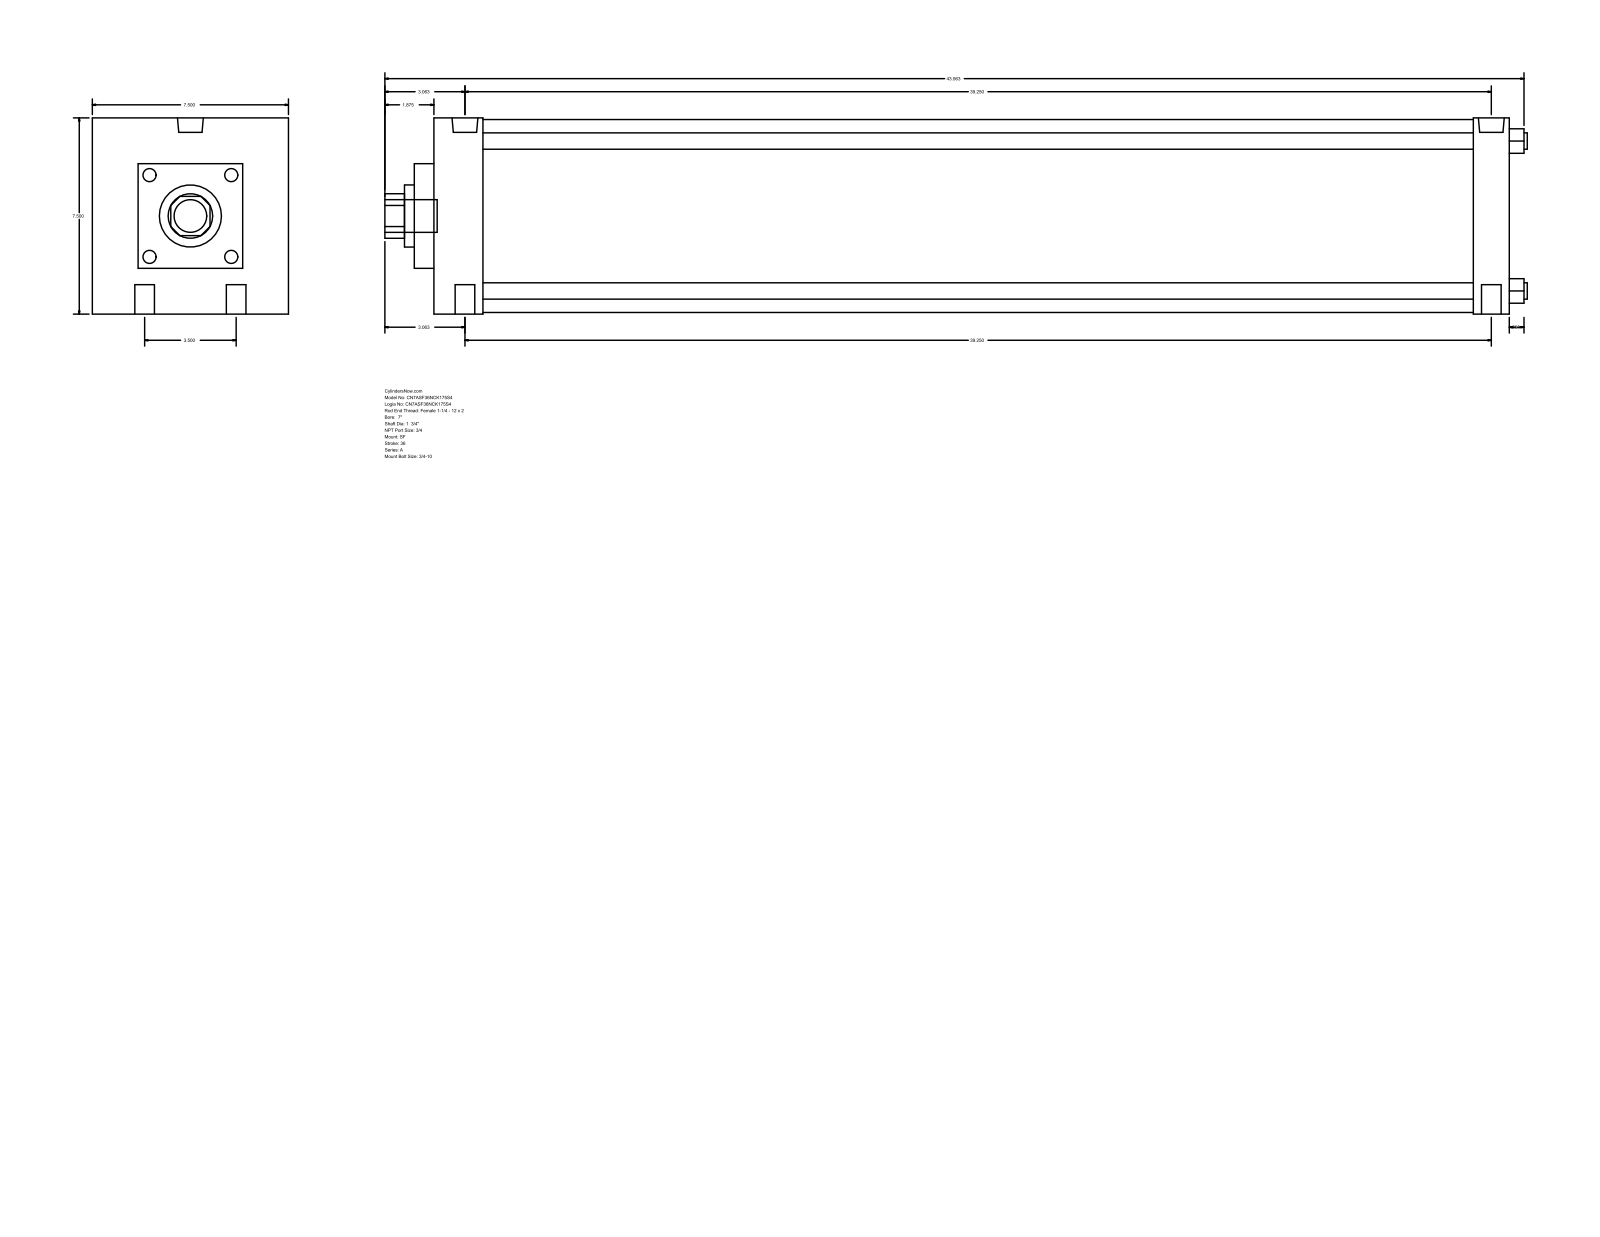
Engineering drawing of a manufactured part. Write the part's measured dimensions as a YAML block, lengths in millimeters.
part_name: "A_SF__0700_1.75"
step_written_by: "GSSL Pune (CONFIG_CONTROL_DESIGN)"
units: millimeters
bodies: {solids: 0, faces: 93, planar: 67, cylindrical: 26, other: 0}
overall_size: [1109.66, 190.5, 190.5]
round_holes:
  - {diameter: 19.05, count: 4}
  - {diameter: 15.08, count: 2}
  - {diameter: 25.12, count: 2}
  - {diameter: 44.45, count: 1}
  - {diameter: 60.33, count: 1}
round_bosses_or_shafts:
  - {diameter: 15.88, count: 4}
  - {diameter: 187.32, count: 1}
  - {diameter: 31.75, count: 1}
partial_cylinders:
  - {radius: 21.63, count: 1}
face_to_face_distances: [190.5, 1044.58, 44.45, 34.92, 19.05, 47.63, 1009.66, 962.03, 996.95, 146.05]
hole_center_spacings: [44.45, 997.94, 996.95, 88.9, 1000.91, 985.83]
